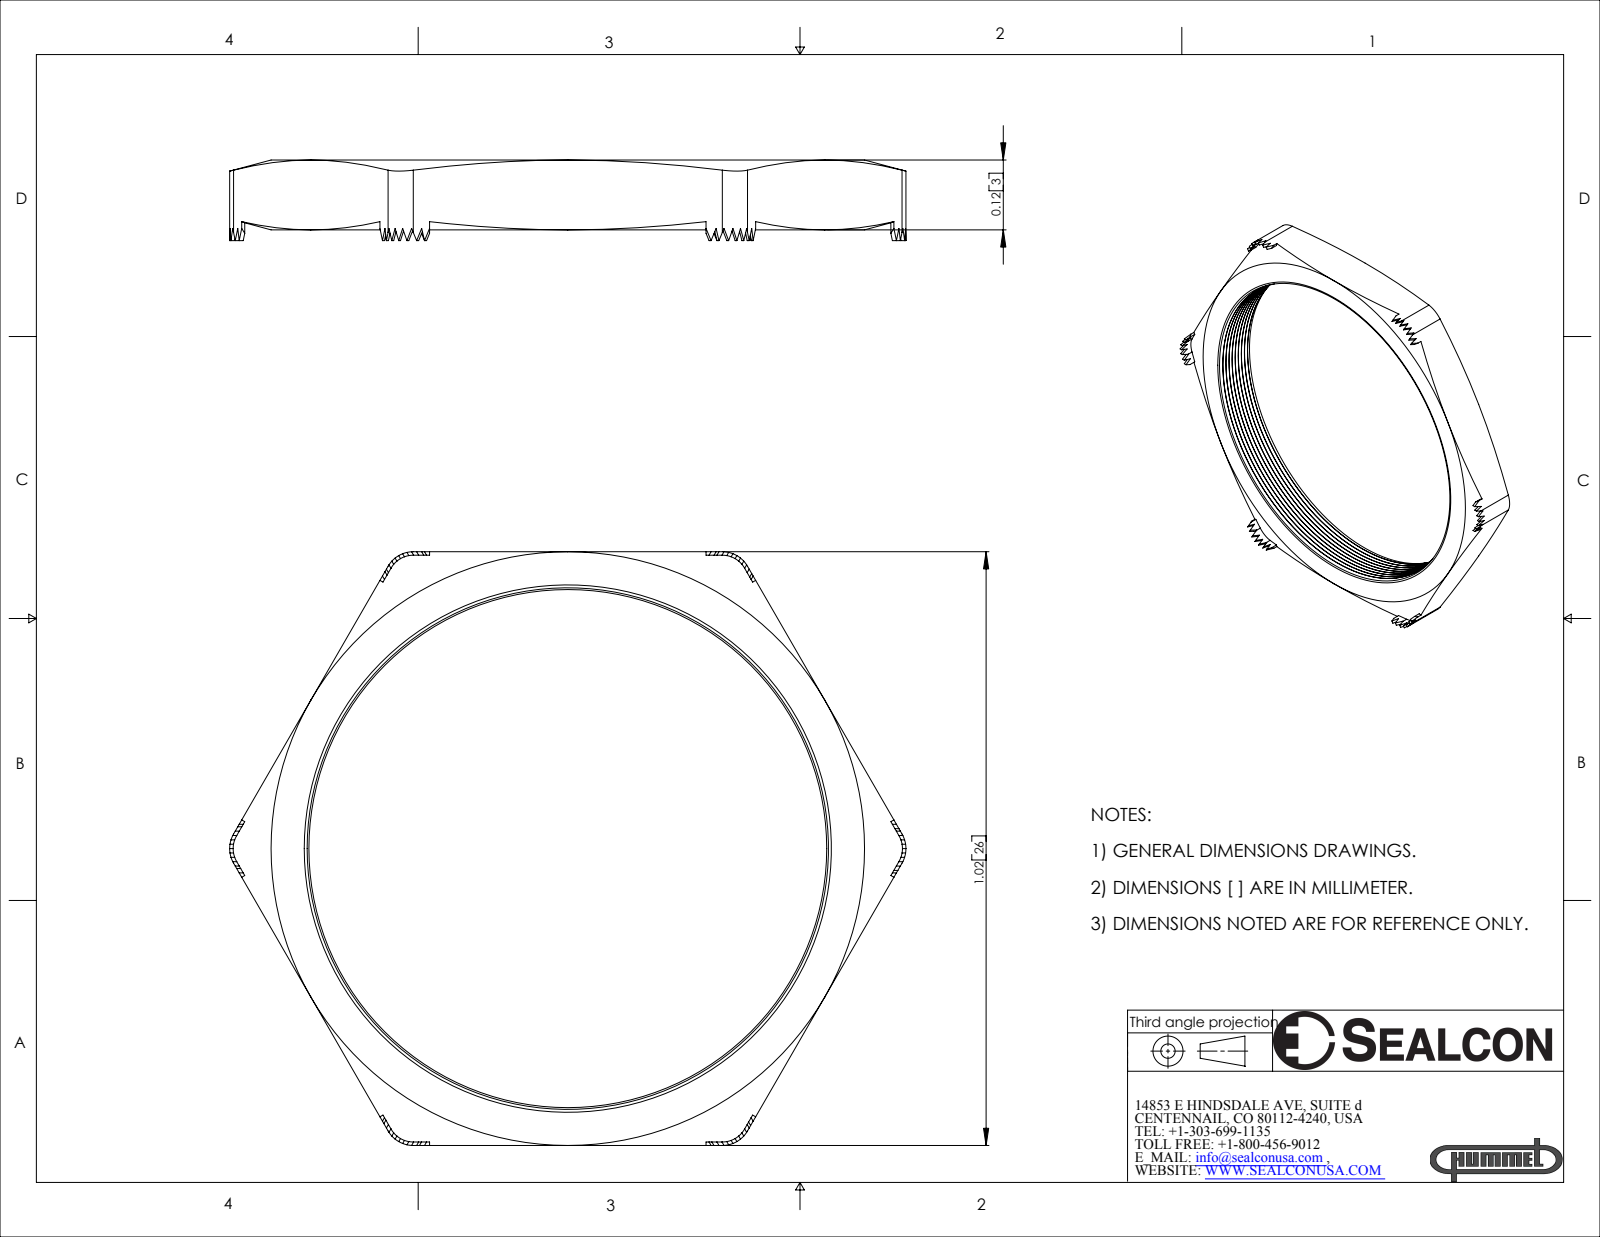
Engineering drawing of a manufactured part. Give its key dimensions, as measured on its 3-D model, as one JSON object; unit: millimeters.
{"part_name": "NP-16-BE", "step_written_by": "SolidWorks 2007 (CONFIG_CONTROL_DESIGN)", "units": "millimeters", "bodies": {"solids": 1, "faces": 206, "planar": 116, "cylindrical": 32, "other": 58}, "overall_size": [29.5, 25.9, 3.5], "volume_mm3": 510, "surface_area_mm2": 1035, "round_holes": [[22.6, 1]], "partial_cylinders_radius": [[1.1, 6], [1.3, 6]], "face_to_face_distances": [25.9, 3, 25.8, 0.4, 25.6, 0.7, 1, 0.6, 1.4, 1.1]}
